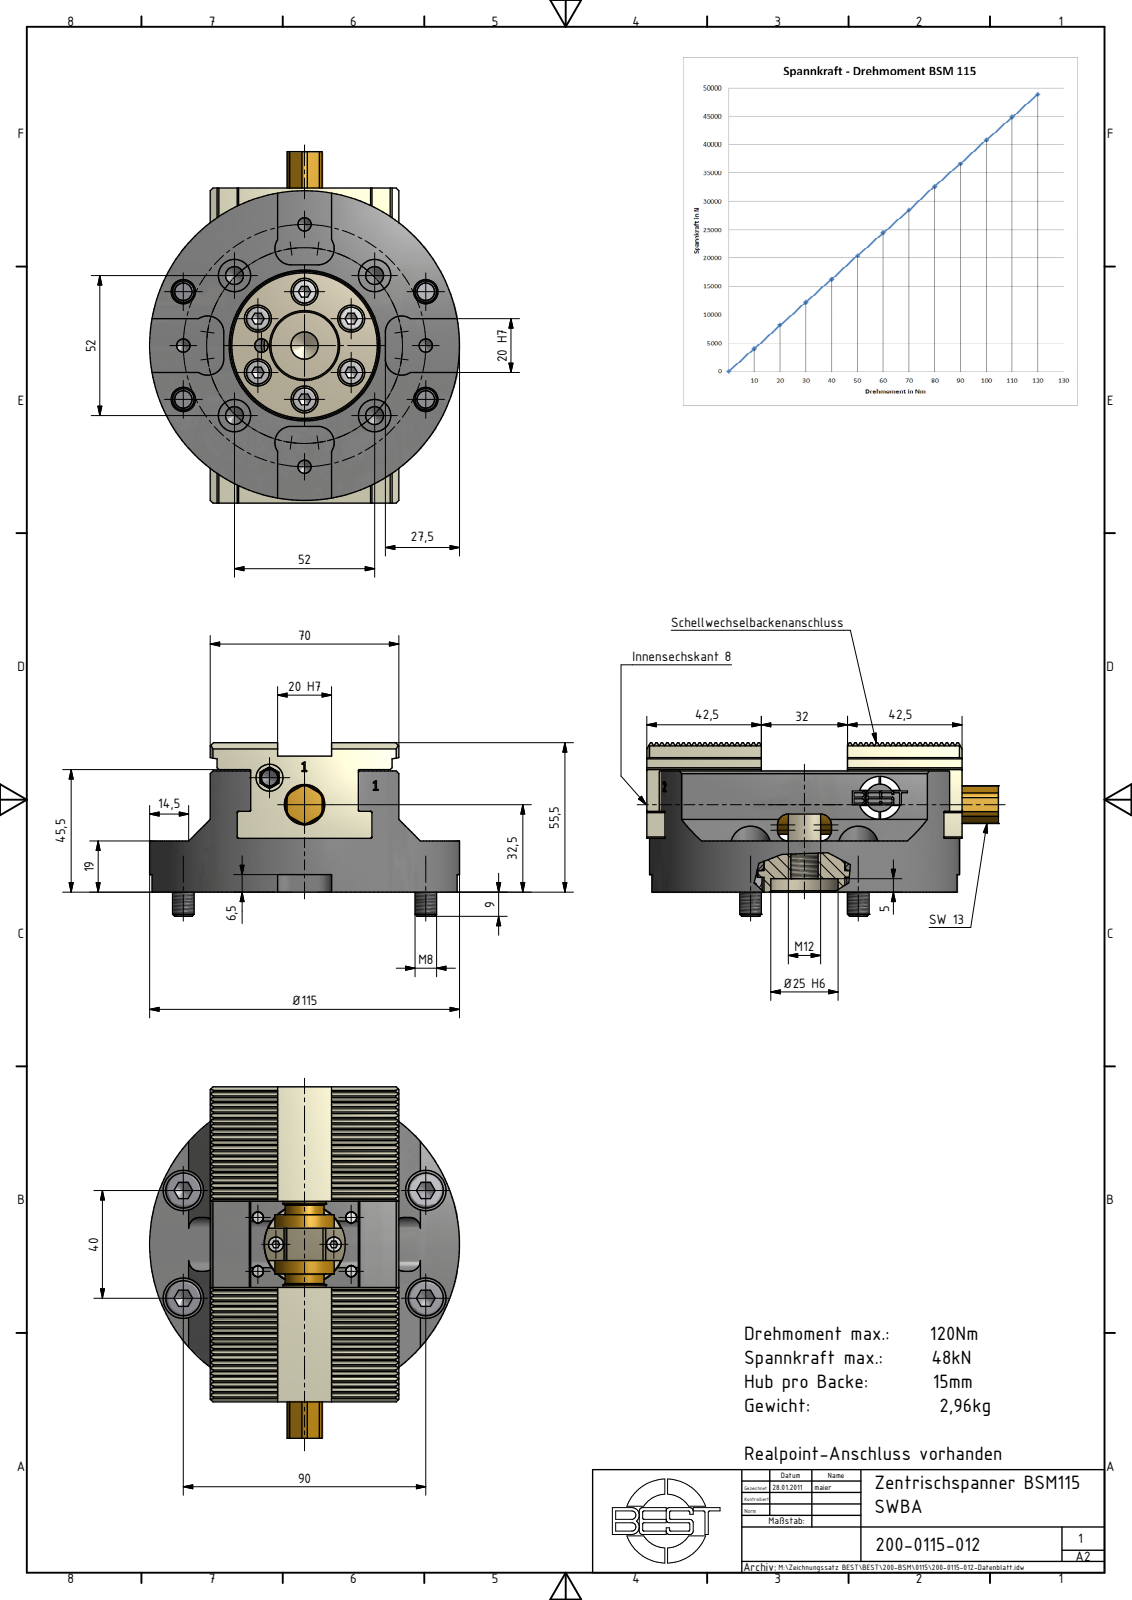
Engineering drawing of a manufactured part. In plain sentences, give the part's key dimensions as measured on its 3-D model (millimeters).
The part is named "200-0115-012-Kunde". Its 3-D file was written by "Autodesk Inventor 2012 (AUTOMOTIVE_DESIGN)". It is 1 solid with 694 faces: 454 planar, 142 cylindrical and 98 other. Overall it measures 136.3 by 115 by 64.5 millimeters. Its volume is 404 397 cubic millimeters and its surface area 69 533 square millimeters. Round holes: 4 of diameter 4.92, 4 of diameter 6.65, 4 of diameter 9, 4 of diameter 12, 4 of diameter 15, 2 of diameter 5, 2 of diameter 10, 1 of diameter 10.11, 1 of diameter 25, 1 of diameter 30, 1 of diameter 55. Round bosses or shafts: 4 of diameter 13, 4 of diameter 8, 2 of diameter 3, 1 of diameter 115, 1 of diameter 54, 1 of diameter 22, 1 of diameter 16. Partial cylindrical surfaces (rounded edges, fillets, slot ends): 24 of radius 0.26, 16 of radius 0.64, 8 of radius 6, 4 of radius 0.8, 4 of radius 1.44, 4 of radius 4, 2 of radius 5.12, 2 of radius 8. The main face-to-face distances are 5, 10, 45, 55.5, 42.5, 26, 74.5, 10.5, 38.5, 19. The hole center spacings are 32.2, 75.61, 19.92, 20, 36.77, 45, 49.24, 49.77.
